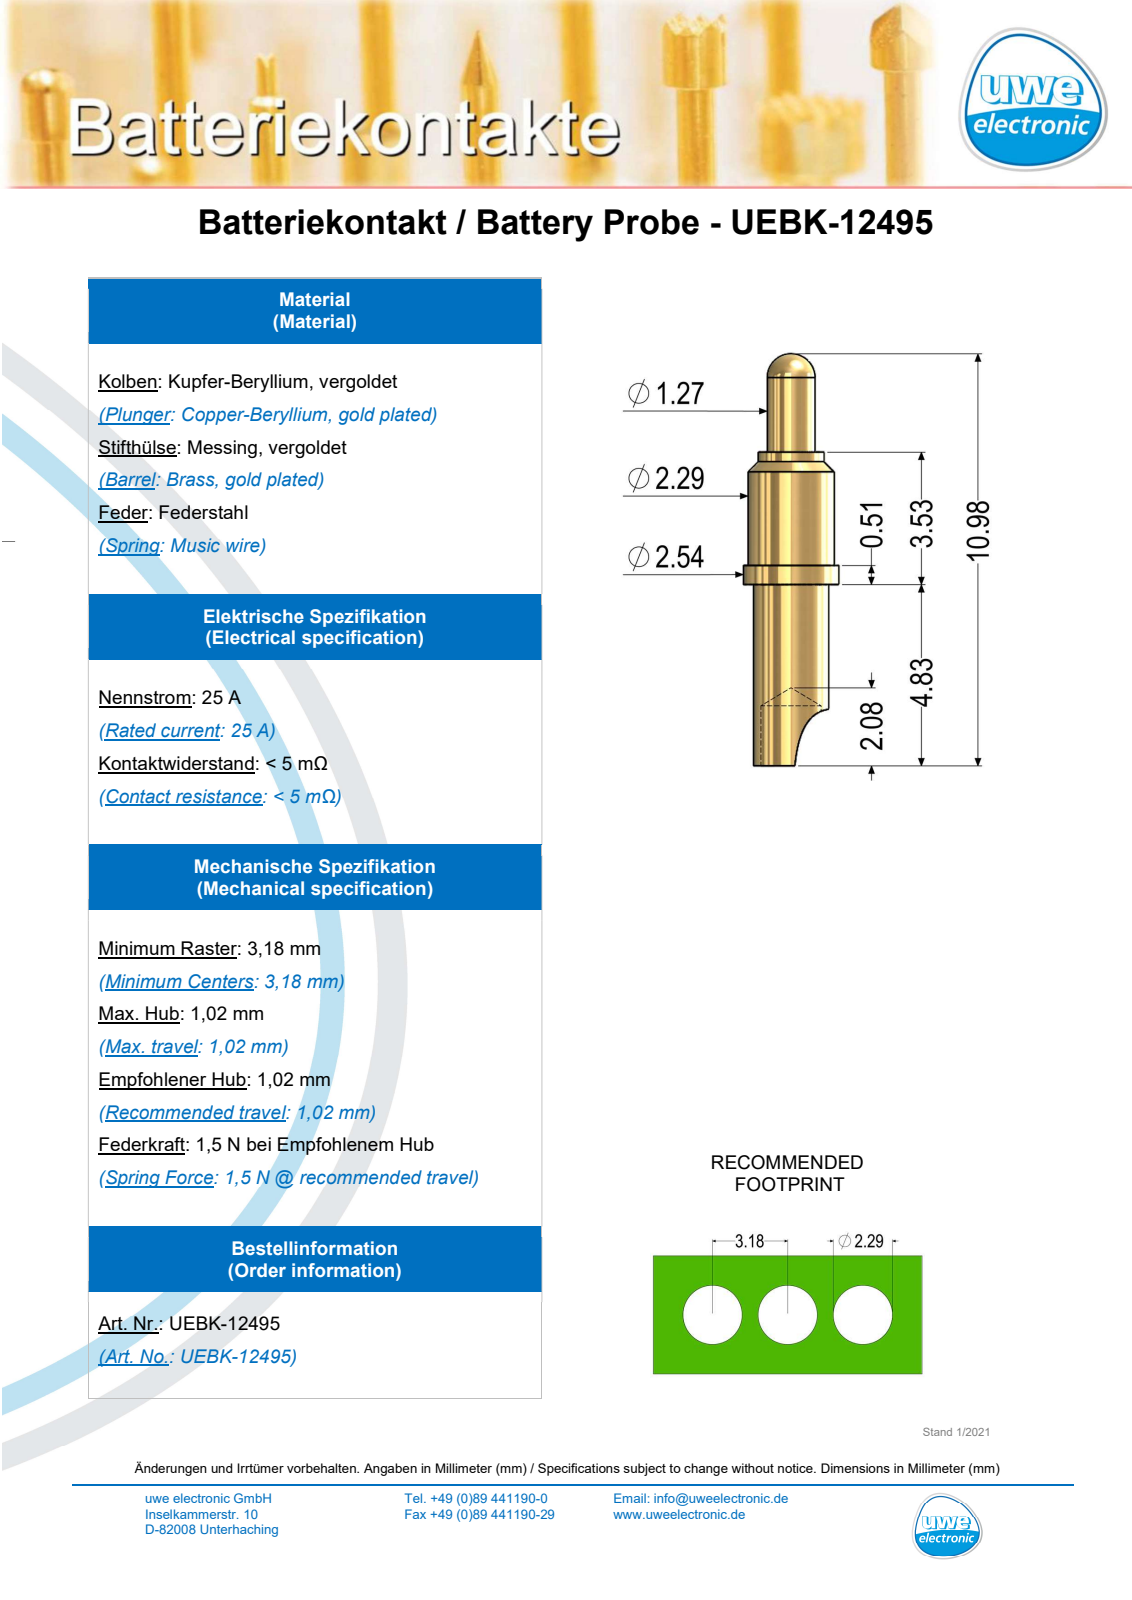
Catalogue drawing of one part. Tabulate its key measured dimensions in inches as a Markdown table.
| quantity | value |
| --- | --- |
| part name | UEBK-12495_2017_09_12 |
| STEP written by | SolidWorks 2017 (AUTOMOTIVE_DESIGN) |
| units | inches |
| bodies | 1 solid, 23 faces (4 planar, 12 cylindrical, 7 other) |
| overall size | 0.432 × 0.1 × 0.1 |
| volume | 0.002 in³ |
| surface area | 0.12 in² |
| round holes (diameter × count) | 0.063 × 1 |
| round bosses / shafts (diameter × count) | 0.1 × 1, 0.09 × 1, 0.079 × 1, 0.069 × 1, 0.05 × 1 |
| main face-to-face distances | 0.139, 0.02, 0.119, 0.19, 0.21, 0.329 |
